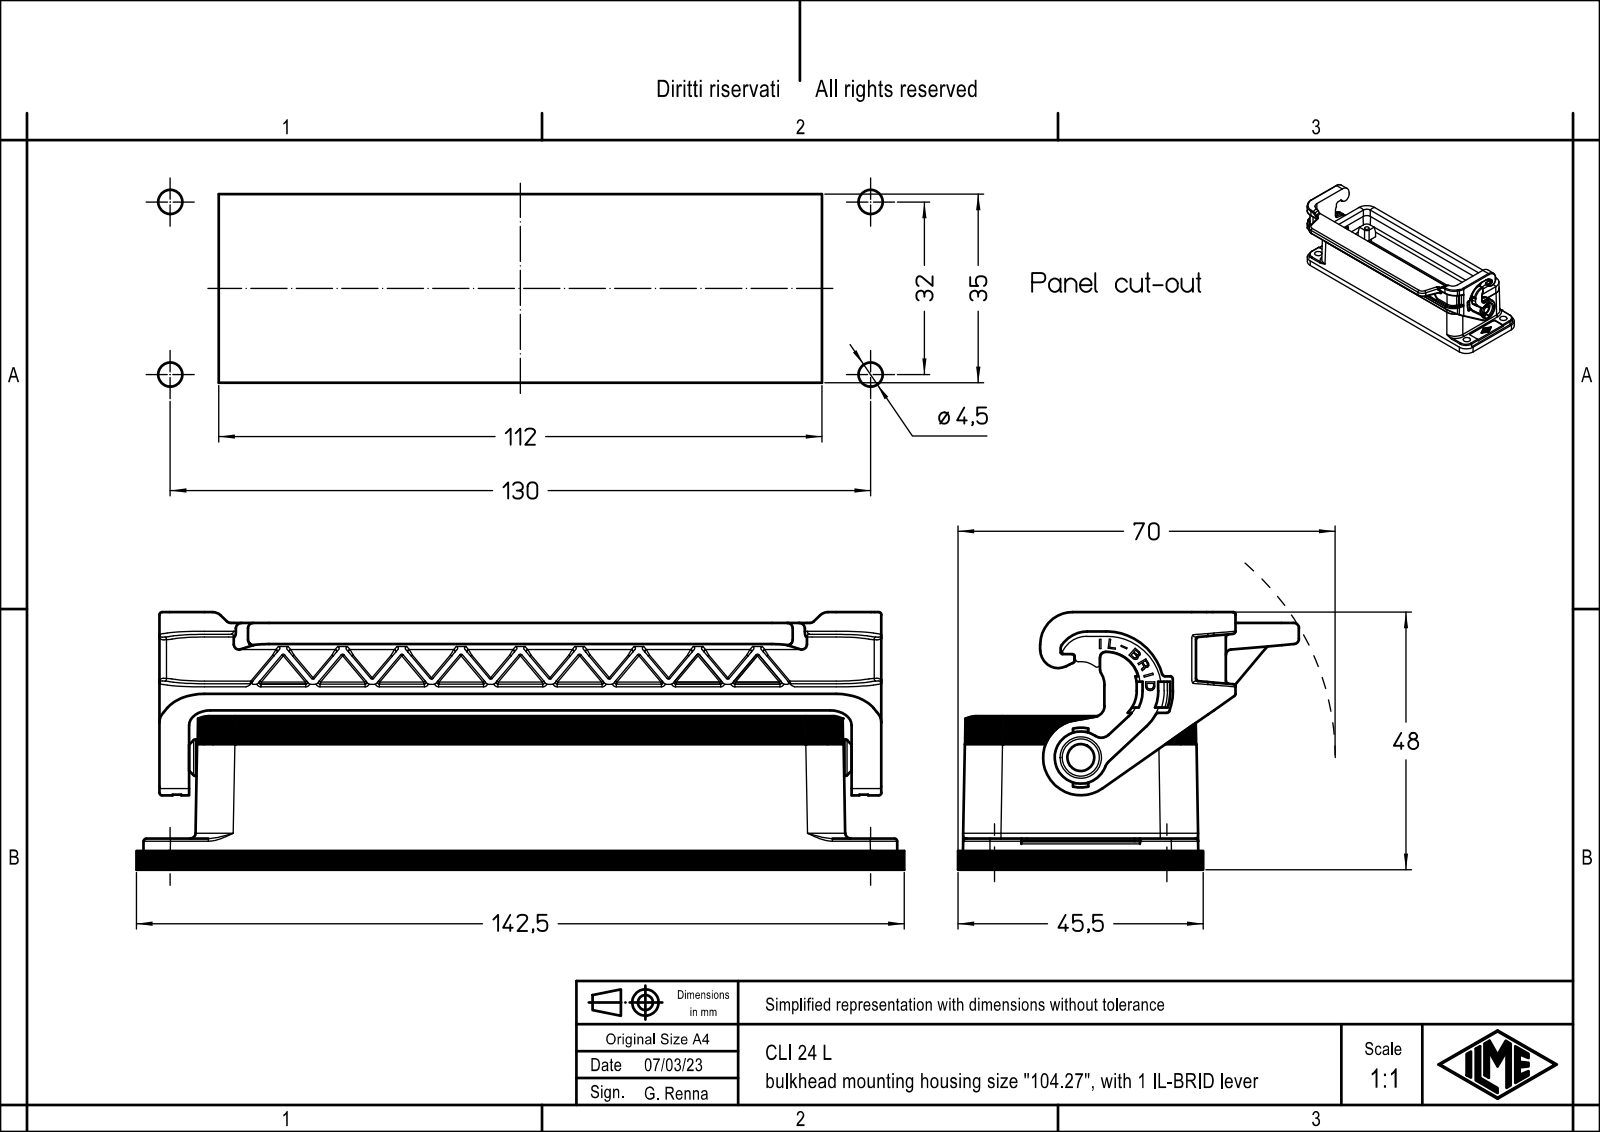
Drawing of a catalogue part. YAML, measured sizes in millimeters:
part_name: "CLI 24 L"
step_written_by: "Creo Elements/Direct Modeling 20.1B 02-Apr-2019 (C) Parametric Technology GmbH (AUTOMOTIVE_DESIGN)"
units: millimeters
bodies: {solids: 1, faces: 1052, planar: 683, cylindrical: 281, other: 88}
overall_size: [142.5, 63.25, 47.8]
volume: 57270
surface_area: 38337
round_holes:
  - {diameter: 3.8, count: 4}
  - {diameter: 4.5, count: 4}
  - {diameter: 3.25, count: 1}
  - {diameter: 5.4, count: 1}
  - {diameter: 7.7, count: 1}
round_bosses_or_shafts:
  - {diameter: 6.9, count: 1}
  - {diameter: 6.8, count: 1}
  - {diameter: 5.2, count: 1}
  - {diameter: 3.2, count: 1}
partial_cylinders:
  - {radius: 0.1, count: 27}
  - {radius: 1, count: 20}
  - {radius: 0.17, count: 15}
  - {radius: 0.2, count: 15}
  - {radius: 2, count: 13}
  - {radius: 4, count: 12}
  - {radius: 0.5, count: 11}
  - {radius: 7, count: 10}
face_to_face_distances: [3.03, 45.8, 40.5, 38.9, 35.93, 38.96, 2.97, 3.5, 5.5, 128.5]
hole_center_spacings: [32, 130, 133.88]
